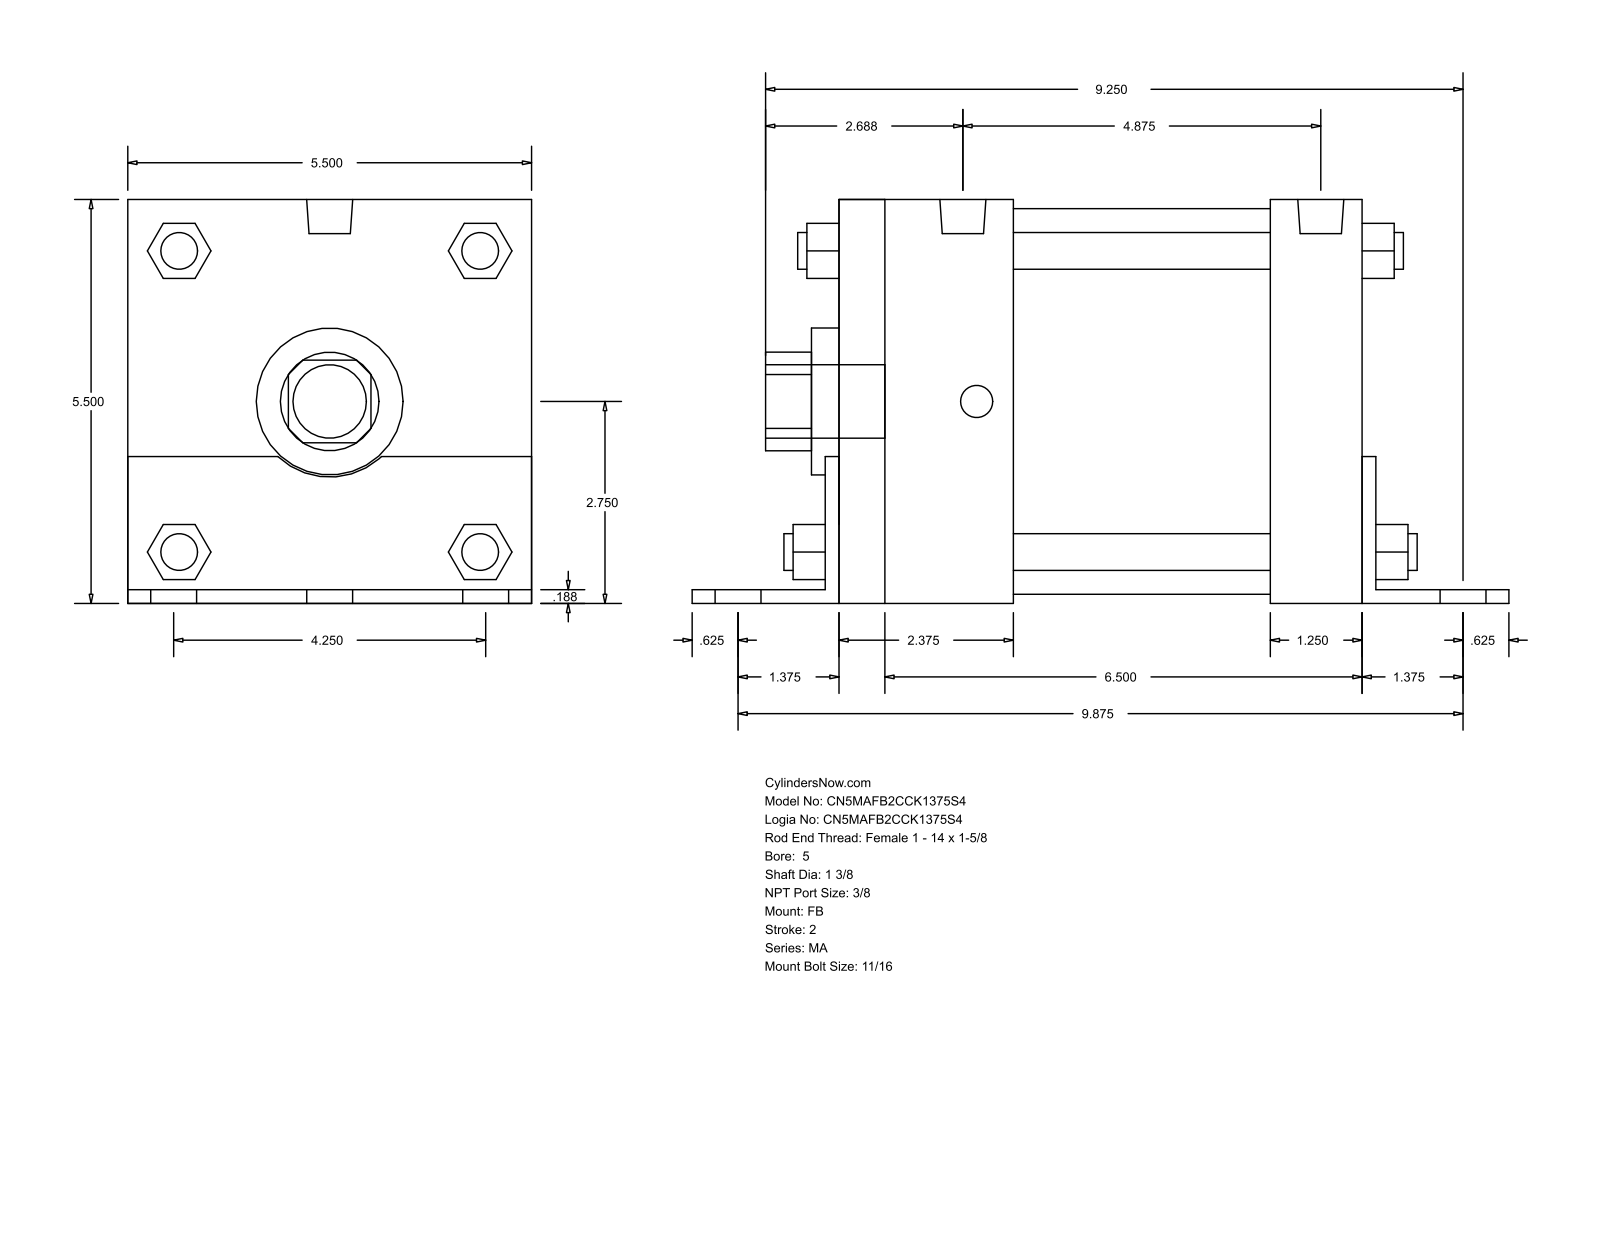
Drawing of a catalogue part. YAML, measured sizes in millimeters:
part_name: "MA_FB__0500_1.375"
step_written_by: "GSSL Pune (CONFIG_CONTROL_DESIGN)"
units: millimeters
bodies: {solids: 0, faces: 140, planar: 105, cylindrical: 35, other: 0}
overall_size: [282.57, 139.75, 139.7]
round_holes:
  - {diameter: 34.92, count: 1}
  - {diameter: 50.8, count: 1}
  - {diameter: 133.35, count: 1}
round_bosses_or_shafts:
  - {diameter: 17.46, count: 6}
  - {diameter: 12.7, count: 4}
  - {diameter: 11.11, count: 4}
  - {diameter: 15.93, count: 2}
  - {diameter: 25.4, count: 1}
partial_cylinders:
  - {radius: 17.06, count: 1}
  - {radius: 26.16, count: 1}
face_to_face_distances: [139.7, 4.76, 139.75, 185.74, 4.71, 134.99, 180.98, 190.5, 36.52, 65.08]
